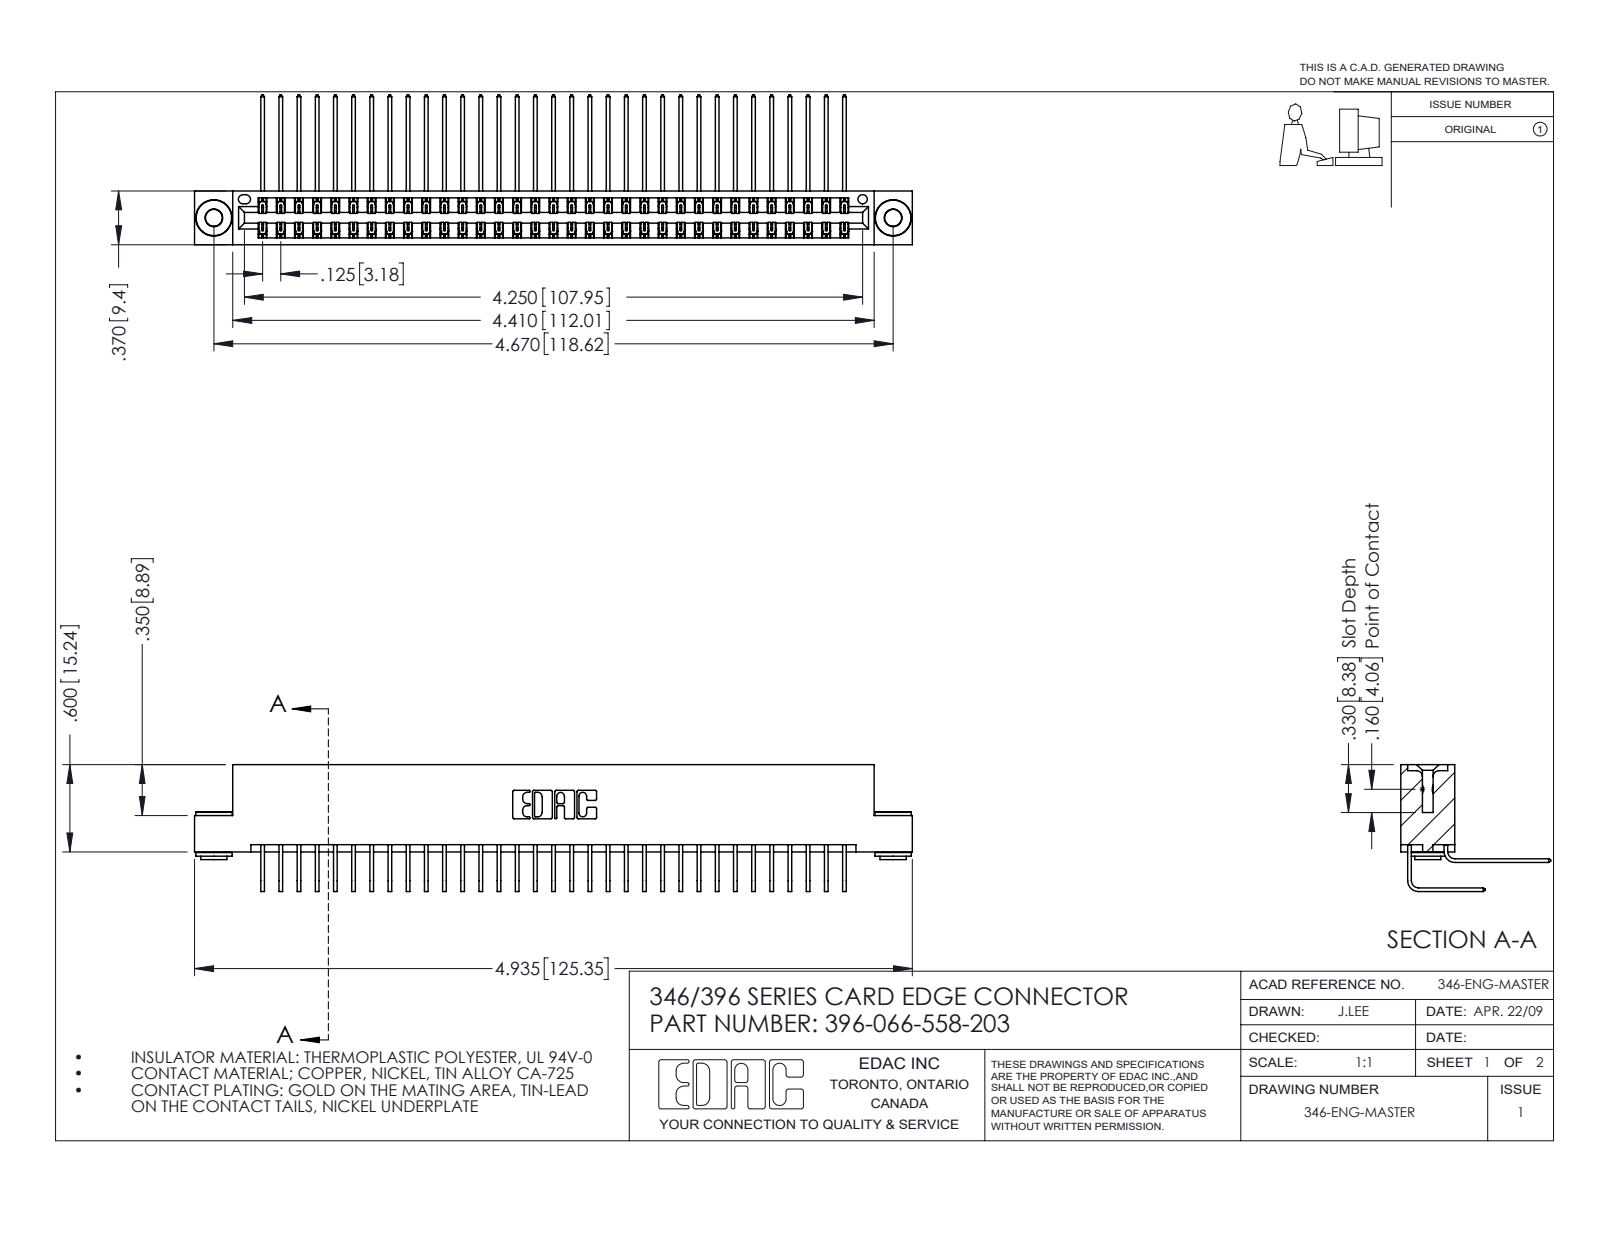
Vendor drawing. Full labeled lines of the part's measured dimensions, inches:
Part name (STEP PRODUCT): 396-066-558-203; 345-292-001_558 559 Tail - 1; 345-250-002_345-250-002-102; 346 Part_Flush Mounting Lugs - 0.156 Dia-TH (+1 more)
STEP written by: SolidWorks 2016 (CONFIG_CONTROL_DESIGN)
Units: inches
Bodies: 69 solids, 3724 faces (2528 planar, 1188 cylindrical, 8 other)
Overall size (bounding box): 4.935 × 1.03 × 0.873
Volume: 0.766 in³ · Surface area: 29.69 in²
Round holes (diameter × count): ⌀0.116 ×2, ⌀0.156 ×2, ⌀0.064 ×1
Round bosses / shafts (diameter × count): ⌀0.25 ×2, ⌀0.18 ×2, ⌀0.136 ×2
Partial cylindrical surfaces — rounded edges, fillets, slot ends (radius × count): R0.006 ×99, R0.01 ×22, R0.007 ×6, R0.031 ×6, R0.026 ×3, R0.014 ×2, R0.022 ×2, R0.024 ×2
Main face-to-face distances: 0.322, 0.048, 0.025, 0.25, 0.37, 0.298, 0.072, 0.275, 0.148, 0.222
Hole centre spacings: 0.246, 4.462, 4.67
